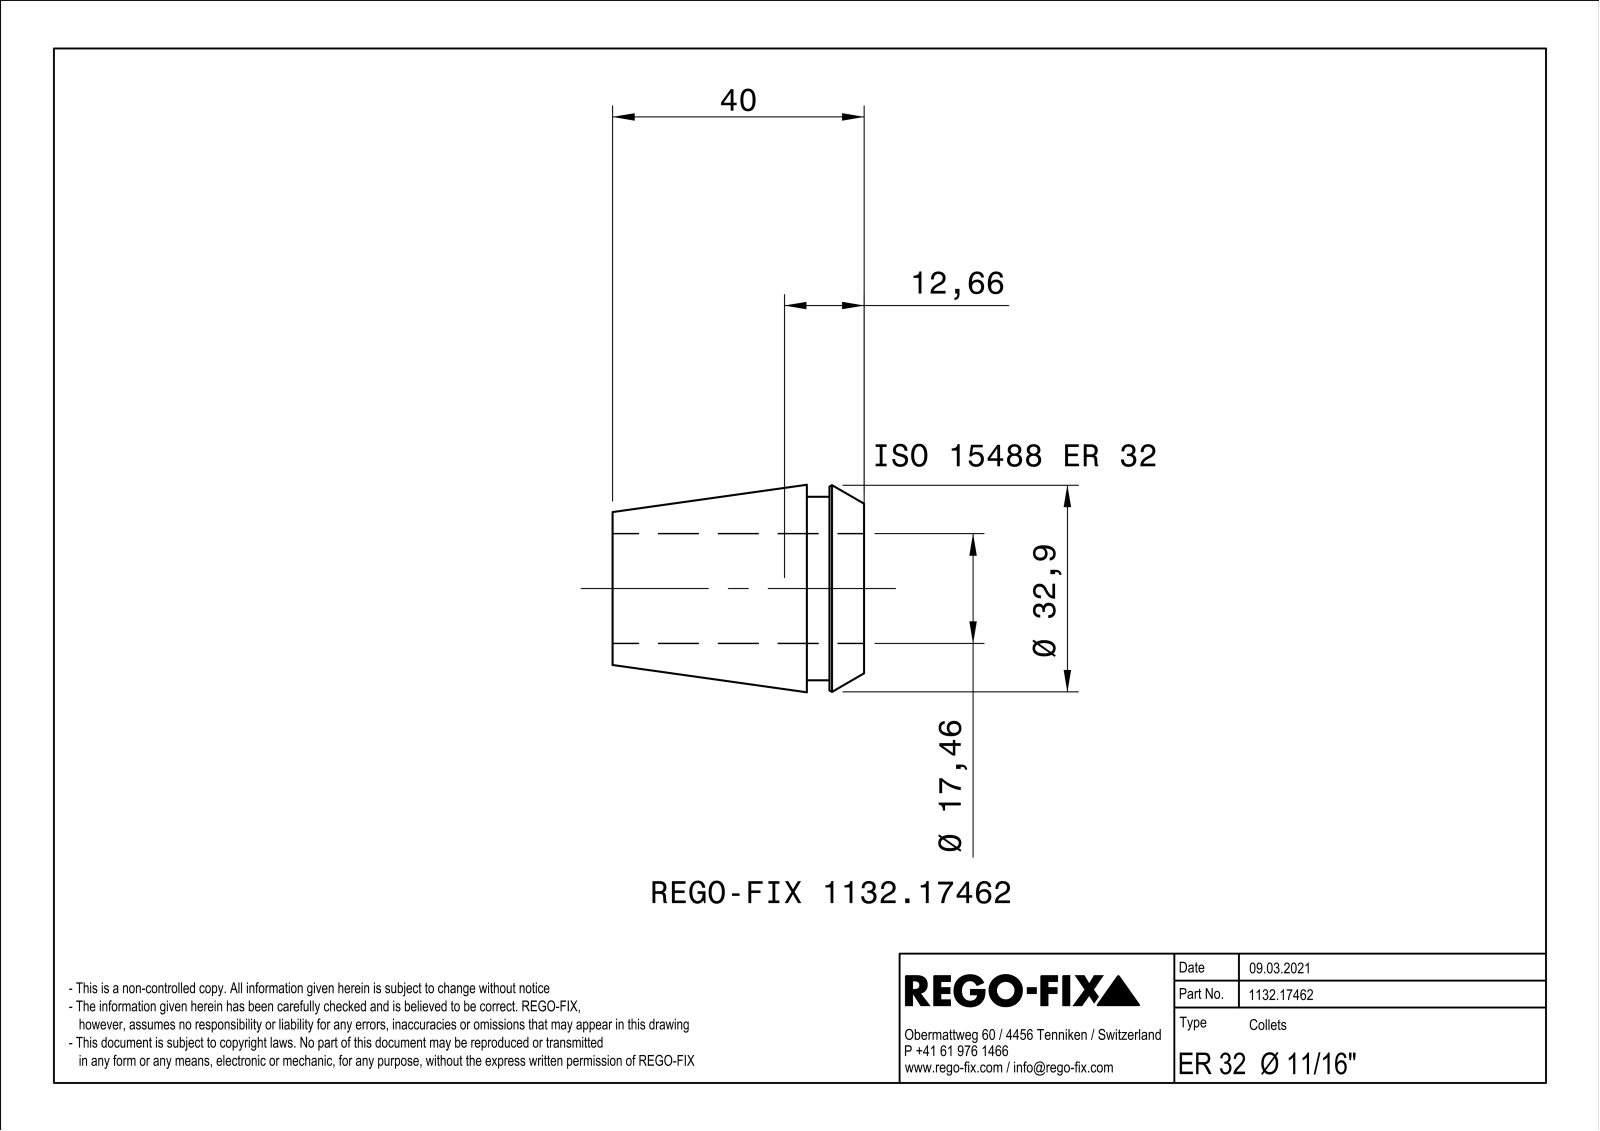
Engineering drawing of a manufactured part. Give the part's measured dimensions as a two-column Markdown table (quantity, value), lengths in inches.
| quantity | value |
| --- | --- |
| part name | NOCUT |
| STEP written by | SIEMENS PLM Software Solid Edge ST10 (AUTOMOTIVE_DESIGN) |
| units | inches |
| bodies | 1 solid, 209 faces (88 planar, 41 cylindrical, 80 other) |
| overall size | 1.575 × 1.298 × 1.298 |
| volume | 0.829 in³ |
| surface area | 18.84 in² |
| round holes (diameter × count) | 0.687 × 1 |
| round bosses / shafts (diameter × count) | 1.15 × 1 |
| partial cylindrical surfaces (radius × count) | 0.016 × 20 |
| main face-to-face distances | 0.039, 1.575, 0.358, 1.217, 0.217, 0.142, 1.358, 0.236, 0.02, 0.122 |
